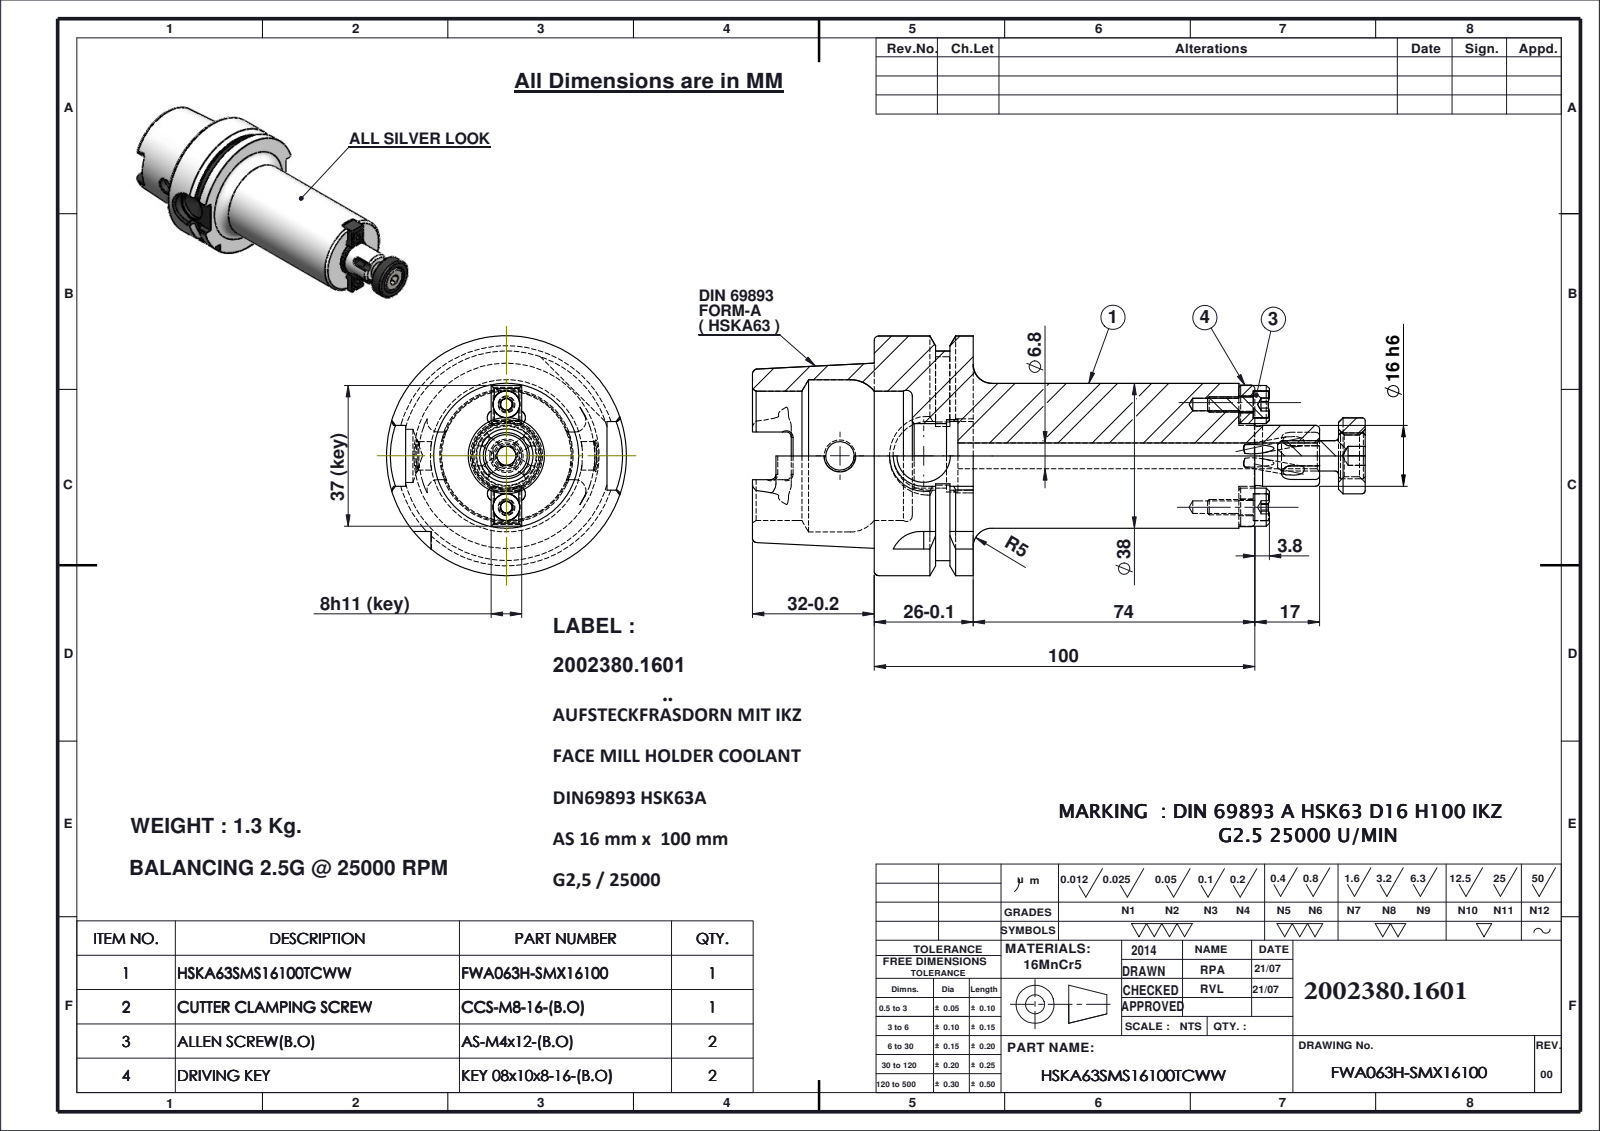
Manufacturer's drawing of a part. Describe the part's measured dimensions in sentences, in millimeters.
The part is named "HSKA63SMS16100TCWW; AS-M4X12_DIN 912 M4 x 10 --- 10N; CCS-M8-16-SHORT LENGHT; CCS-M8-16-1-SHORT LENGHT (+3 more)". Its 3-D file was written by "SolidWorks 2009 (CONFIG_CONTROL_DESIGN)". It is 7 solids with 363 faces: 145 planar, 95 cylindrical and 123 other. Overall it measures 161 by 63 by 63 millimeters. Its volume is 168 737 cubic millimeters and its surface area 37 993 square millimeters. Round holes: 4 of diameter 3, 2 of diameter 3.3, 2 of diameter 4.4, 2 of diameter 7.1, 1 of diameter 6.8, 1 of diameter 7.5, 1 of diameter 11, 1 of diameter 14, 1 of diameter 17, 1 of diameter 19, 1 of diameter 34, 1 of diameter 40. Round bosses or shafts: 2 of diameter 7, 2 of diameter 4, 1 of diameter 63, 1 of diameter 55, 1 of diameter 38, 1 of diameter 20, 1 of diameter 16, 1 of diameter 15.6. Partial cylindrical surfaces (rounded edges, fillets, slot ends): 8 of radius 2, 6 of radius 1.3, 4 of radius 2.88, 2 of radius 8, 1 of radius 9. The main face-to-face distances are 26, 100, 10, 74, 16, 90, 32, 42, 58, 132. The hole center spacings are 13.5, 22, 27.
